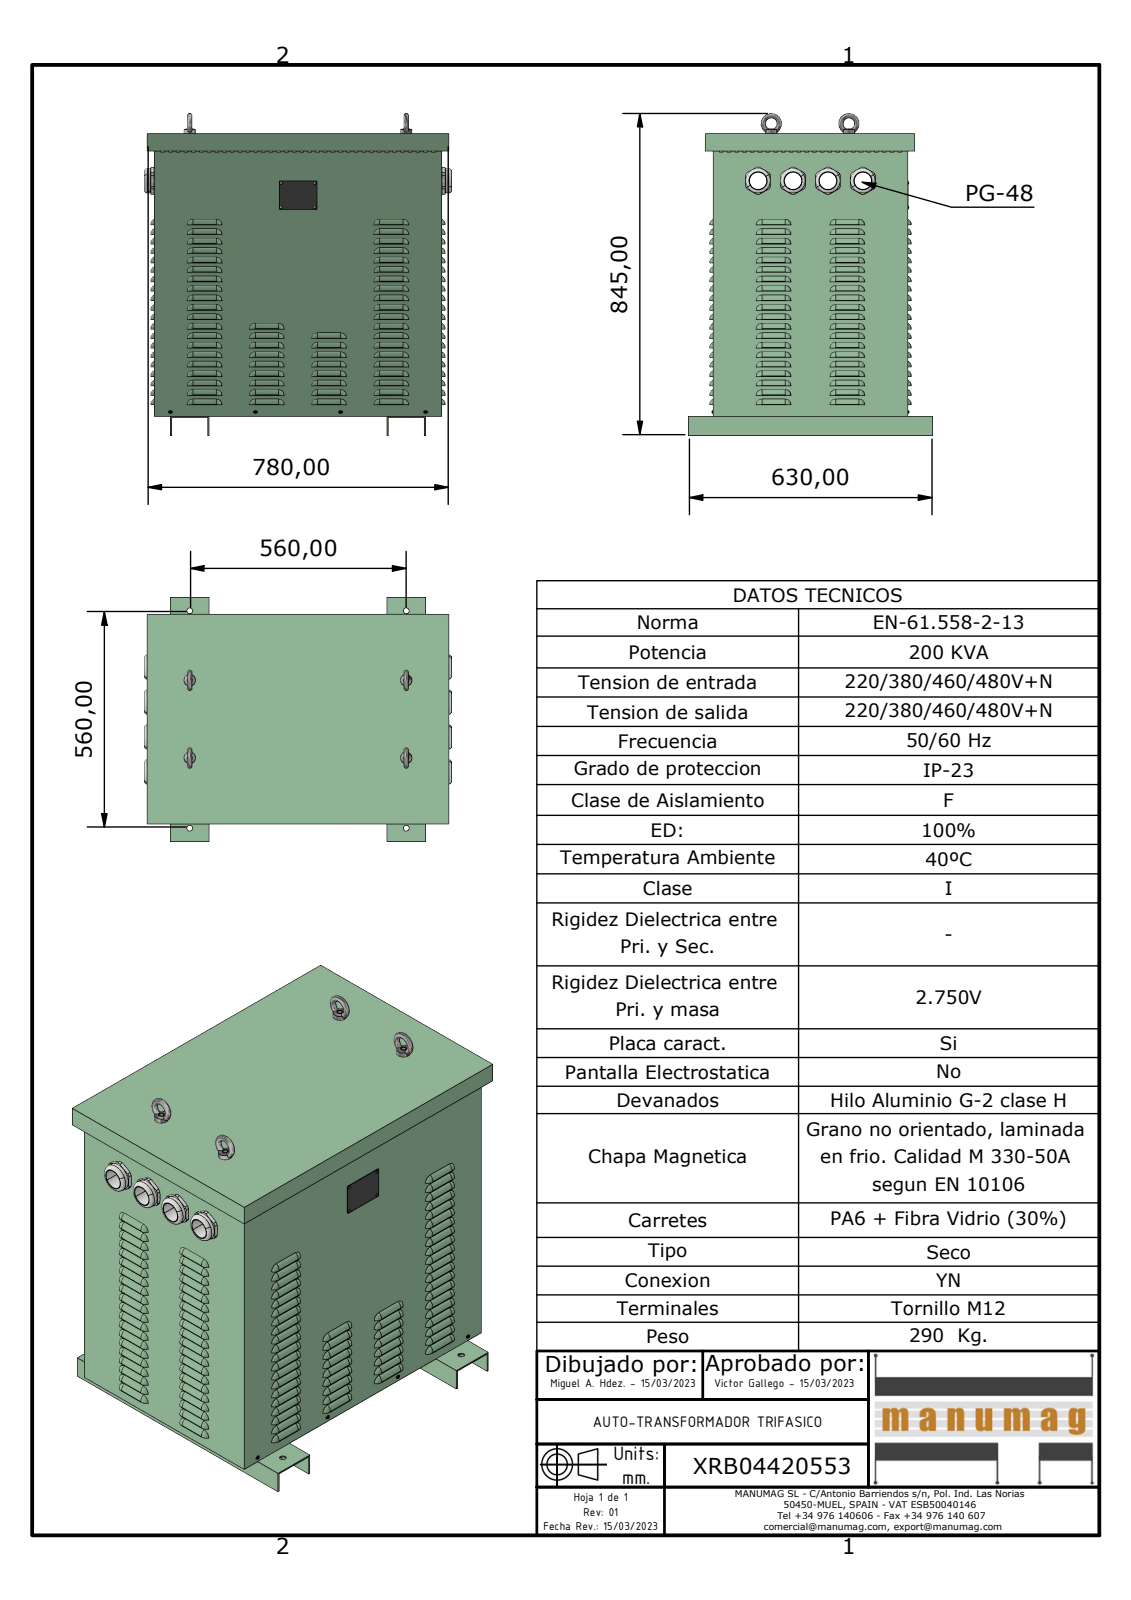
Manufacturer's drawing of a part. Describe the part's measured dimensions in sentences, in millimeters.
The part is named "XRB04420553; JE200 CUERPO; JE160 EXPORT JE200 EXPORT NACIONAL BASE; JE160 EXPORT JE200 EXPORT NACIONAL PATA (+6 more)". Its 3-D file was written by "Autodesk Inventor 2023 (AUTOMOTIVE_DESIGN)". It is 30 solids with 4663 faces: 1571 planar, 1992 cylindrical and 1100 other. Overall it measures 835 by 795.27 by 630 millimeters. Its volume is 7 588 000 cubic millimeters and its surface area 6 374 000 square millimeters. Round holes: 936 of diameter 11, 12 of diameter 15, 4 of diameter 4, 4 of diameter 5, 4 of diameter 10.11, 4 of diameter 44, 4 of diameter 60. Round bosses or shafts: 4 of diameter 63, 4 of diameter 59.3, 4 of diameter 59.15, 4 of diameter 57.63, 4 of diameter 30, 4 of diameter 4, 4 of diameter 3.62, 4 of diameter 3.2. Partial cylindrical surfaces (rounded edges, fillets, slot ends): 194 of radius 14, 80 of radius 7, 80 of radius 15, 8 of radius 2.5, 4 of radius 2, 4 of radius 35. The main face-to-face distances are 2, 500, 730, 742, 498, 502, 732, 740, 728, 744. The hole center spacings are 15, 30, 33.54, 204.55, 159.71, 204, 129.87, 159.
